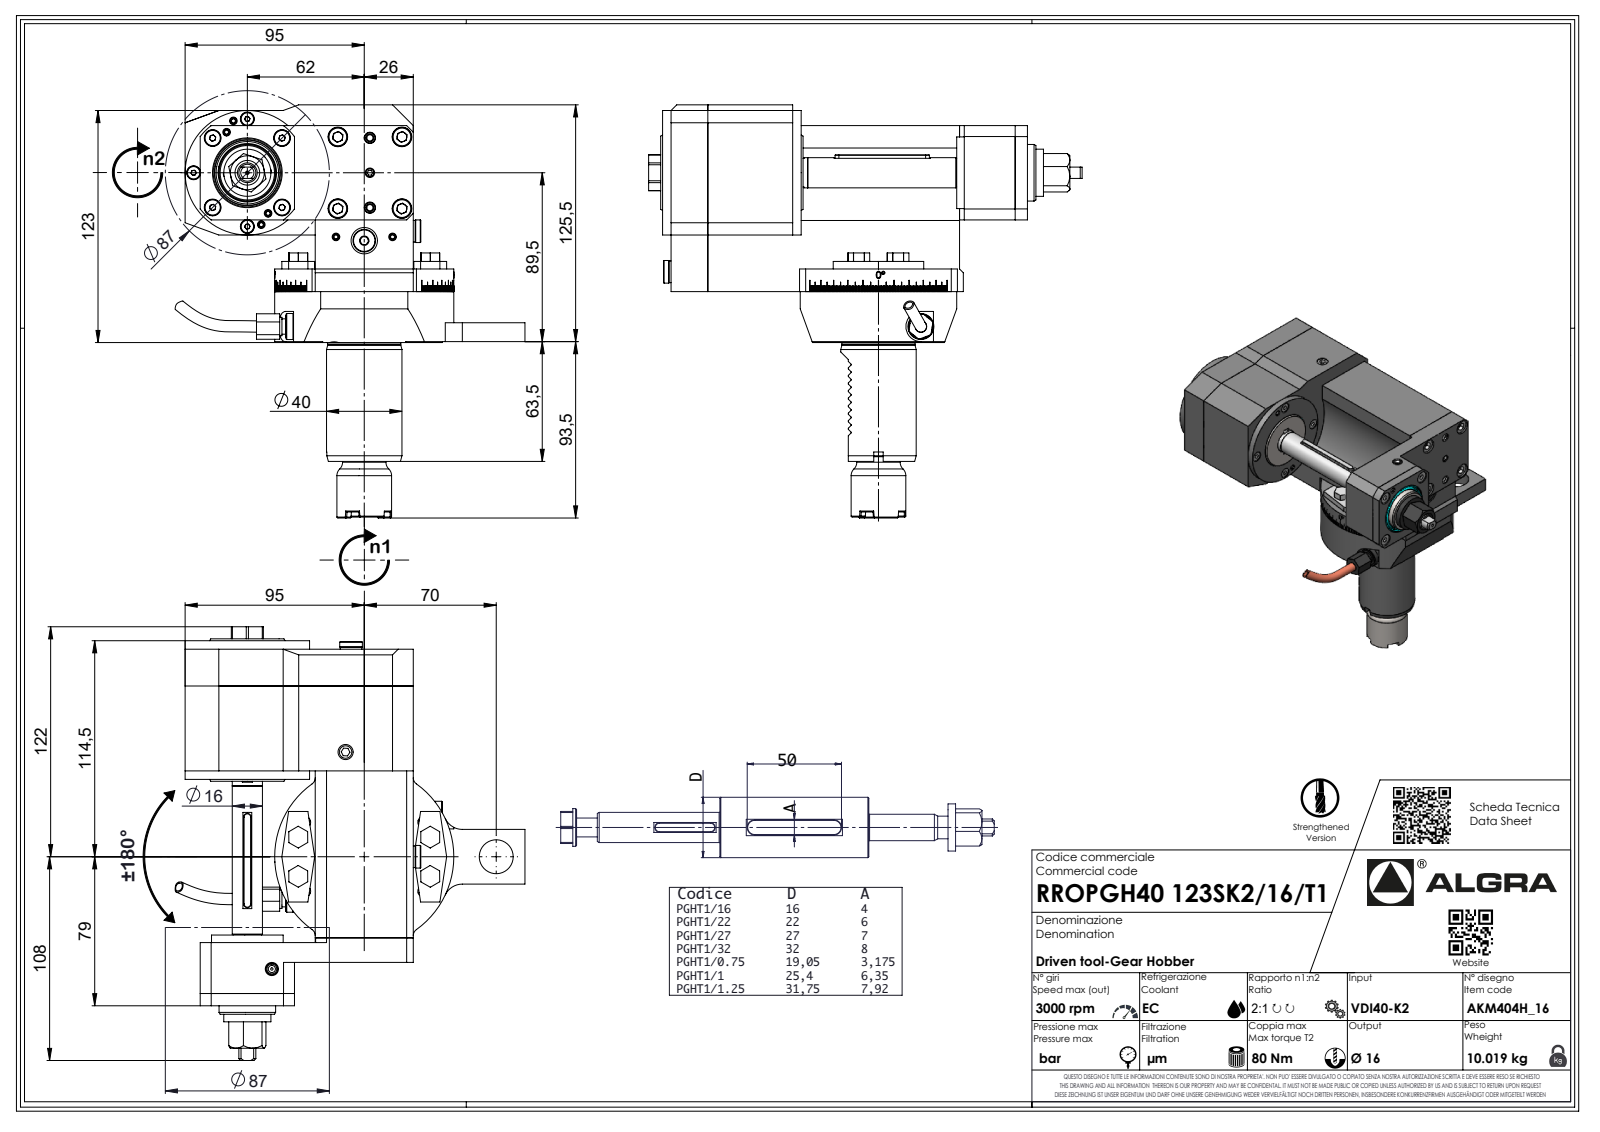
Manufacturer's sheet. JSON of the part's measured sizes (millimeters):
{"part_name": "RROPGH40123SK216T1", "step_written_by": "SolidWorks 2023 (AUTOMOTIVE_DESIGN)", "units": "millimeters", "bodies": {"solids": 5, "faces": 1763, "planar": 1472, "cylindrical": 97, "other": 194}, "overall_size": [229.9, 219, 185.52], "volume_mm3": 1488000, "surface_area_mm2": 125647, "round_holes": [[2.1, 1], [8.57, 1], [12, 1], [14.2, 1], [20, 1]], "round_bosses_or_shafts": [[66, 1], [40, 1], [38.7, 1], [38, 1], [30, 1], [29, 1], [25, 1], [23, 1]], "partial_cylinders_radius": [[0.3, 10], [0.33, 7], [0.52, 7], [3.7, 7], [4, 4], [0.25, 2], [2, 2], [8, 2]], "face_to_face_distances": [69, 58, 8, 11, 64.5, 87, 52, 4.5, 27, 88], "hole_center_spacings": [32, 132.99]}
